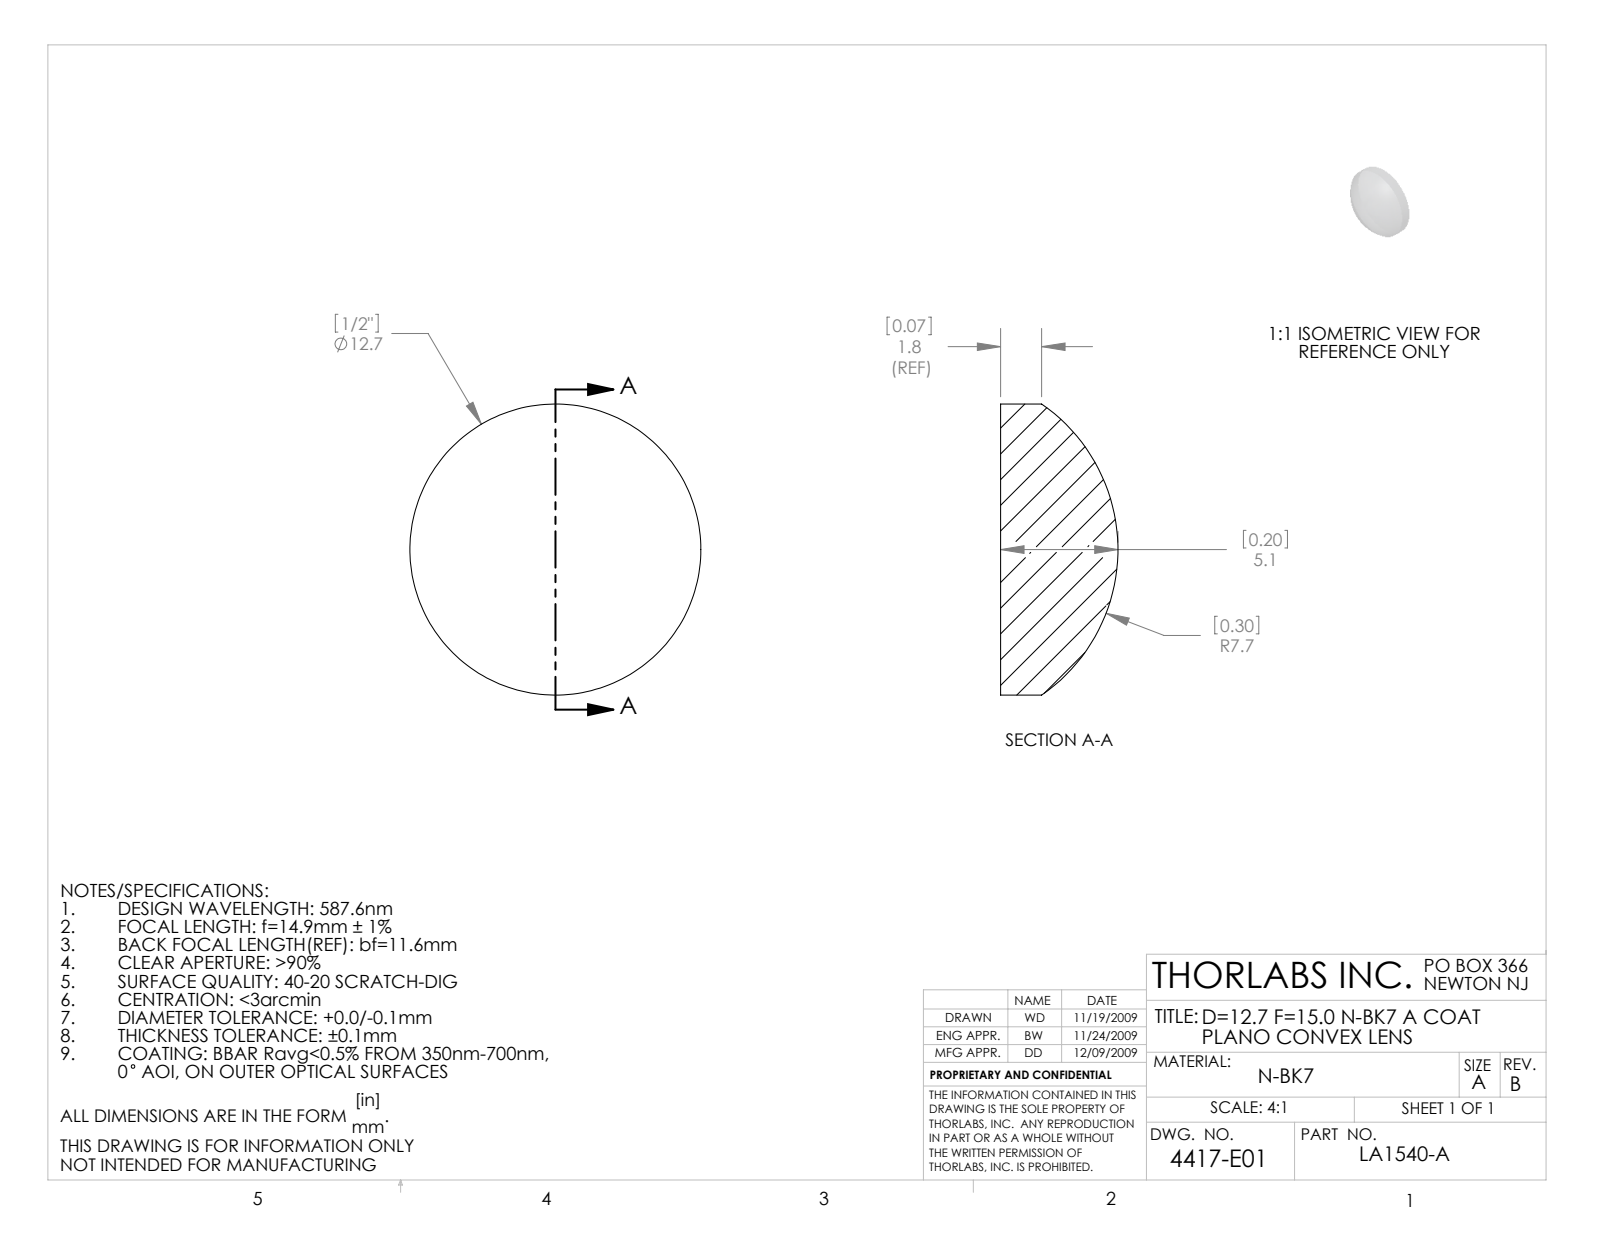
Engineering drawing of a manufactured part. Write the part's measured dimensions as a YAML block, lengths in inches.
part_name: "4417-E0W"
step_written_by: "SolidWorks 2009 (AUTOMOTIVE_DESIGN)"
units: inches
bodies: {solids: 1, faces: 5, planar: 1, cylindrical: 2, other: 2}
overall_size: [0.5, 0.5, 0.202]
volume: 0.028
surface_area: 0.558
round_bosses_or_shafts:
  - {diameter: 0.5, count: 1}
